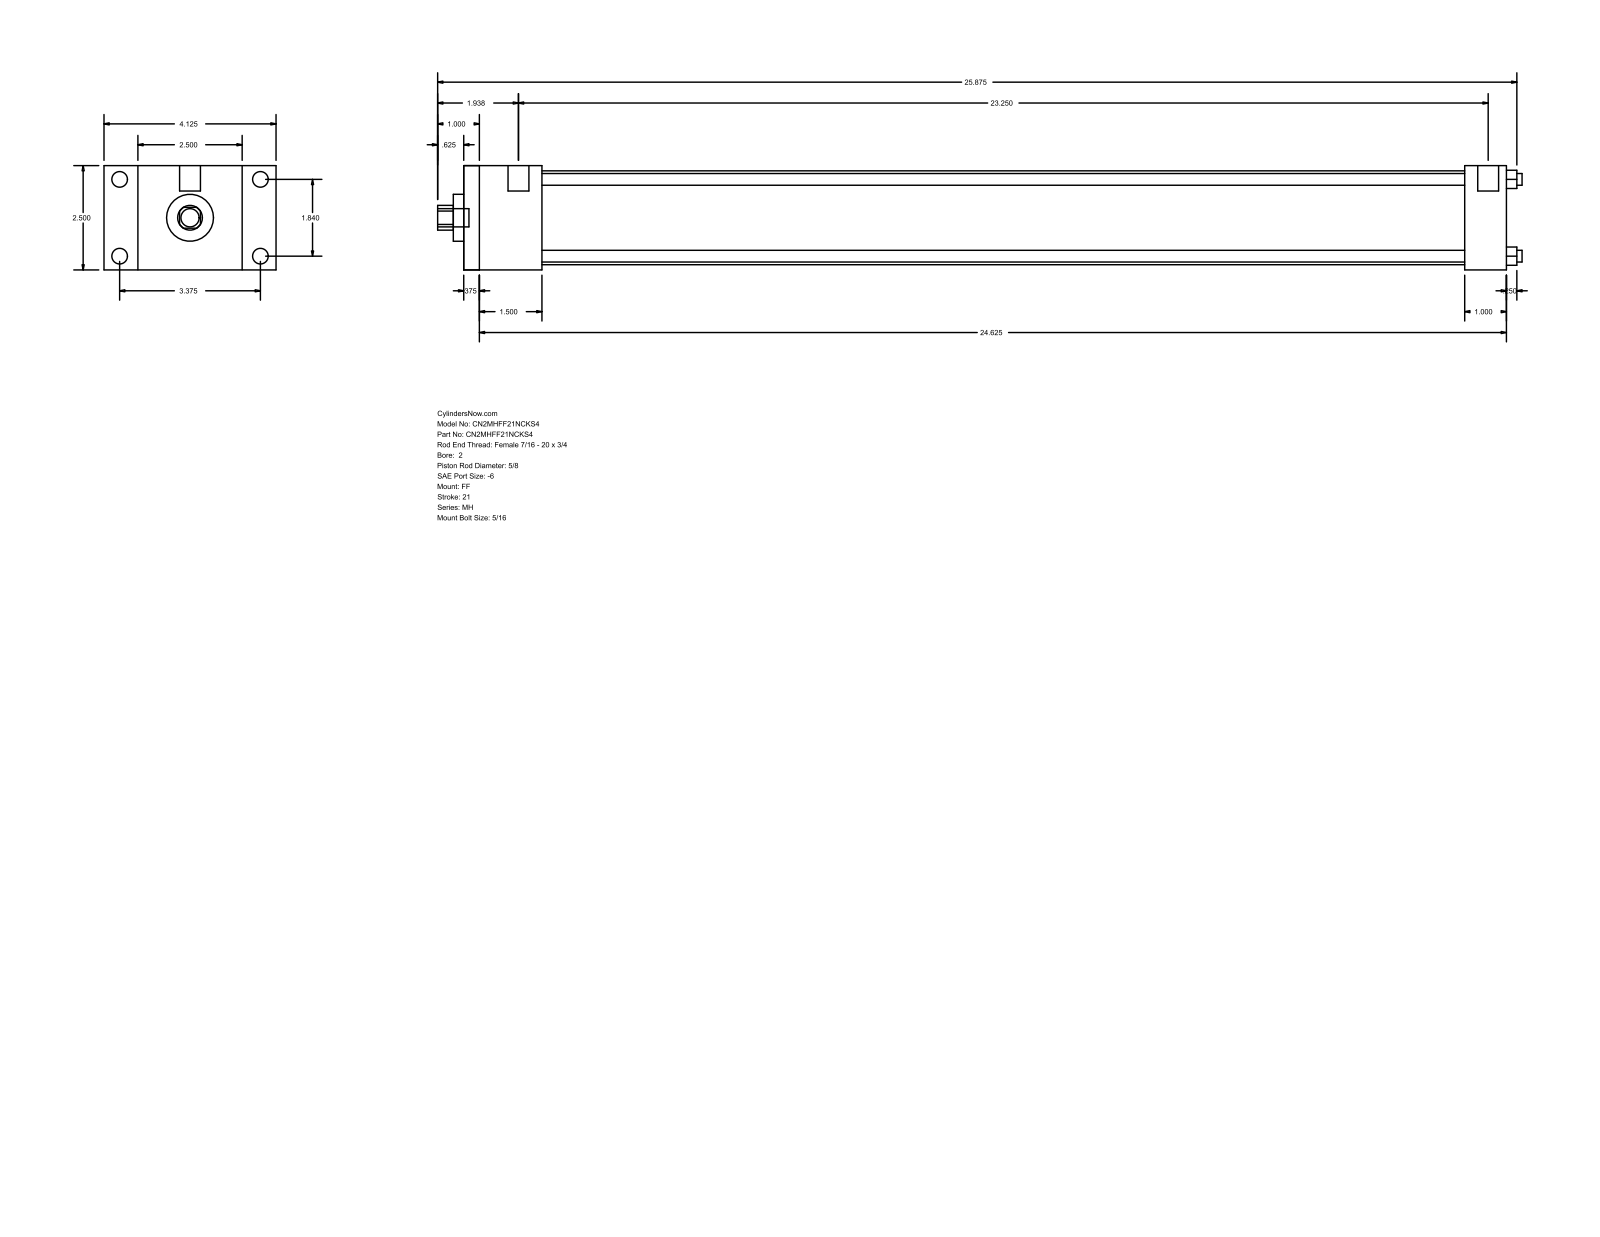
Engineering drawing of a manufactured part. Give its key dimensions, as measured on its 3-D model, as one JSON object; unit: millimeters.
{"part_name": "MH_FF__0200_0.625", "step_written_by": "GSSL Pune (CONFIG_CONTROL_DESIGN)", "units": "millimeters", "bodies": {"solids": 0, "faces": 92, "planar": 64, "cylindrical": 28, "other": 0}, "overall_size": [660.4, 104.78, 63.5], "round_holes": [[7.14, 4], [15.88, 1], [28.57, 1], [57.15, 1]], "round_bosses_or_shafts": [[9.53, 4], [5.56, 4], [12.7, 2], [11.11, 1]], "partial_cylinders_radius": [[7.54, 1]], "face_to_face_distances": [63.5, 635, 9.52, 625.48, 25.4, 38.1, 47.62, 609.6, 600.08, 561.98], "hole_center_spacings": [33.05, 46.74, 66.1]}
